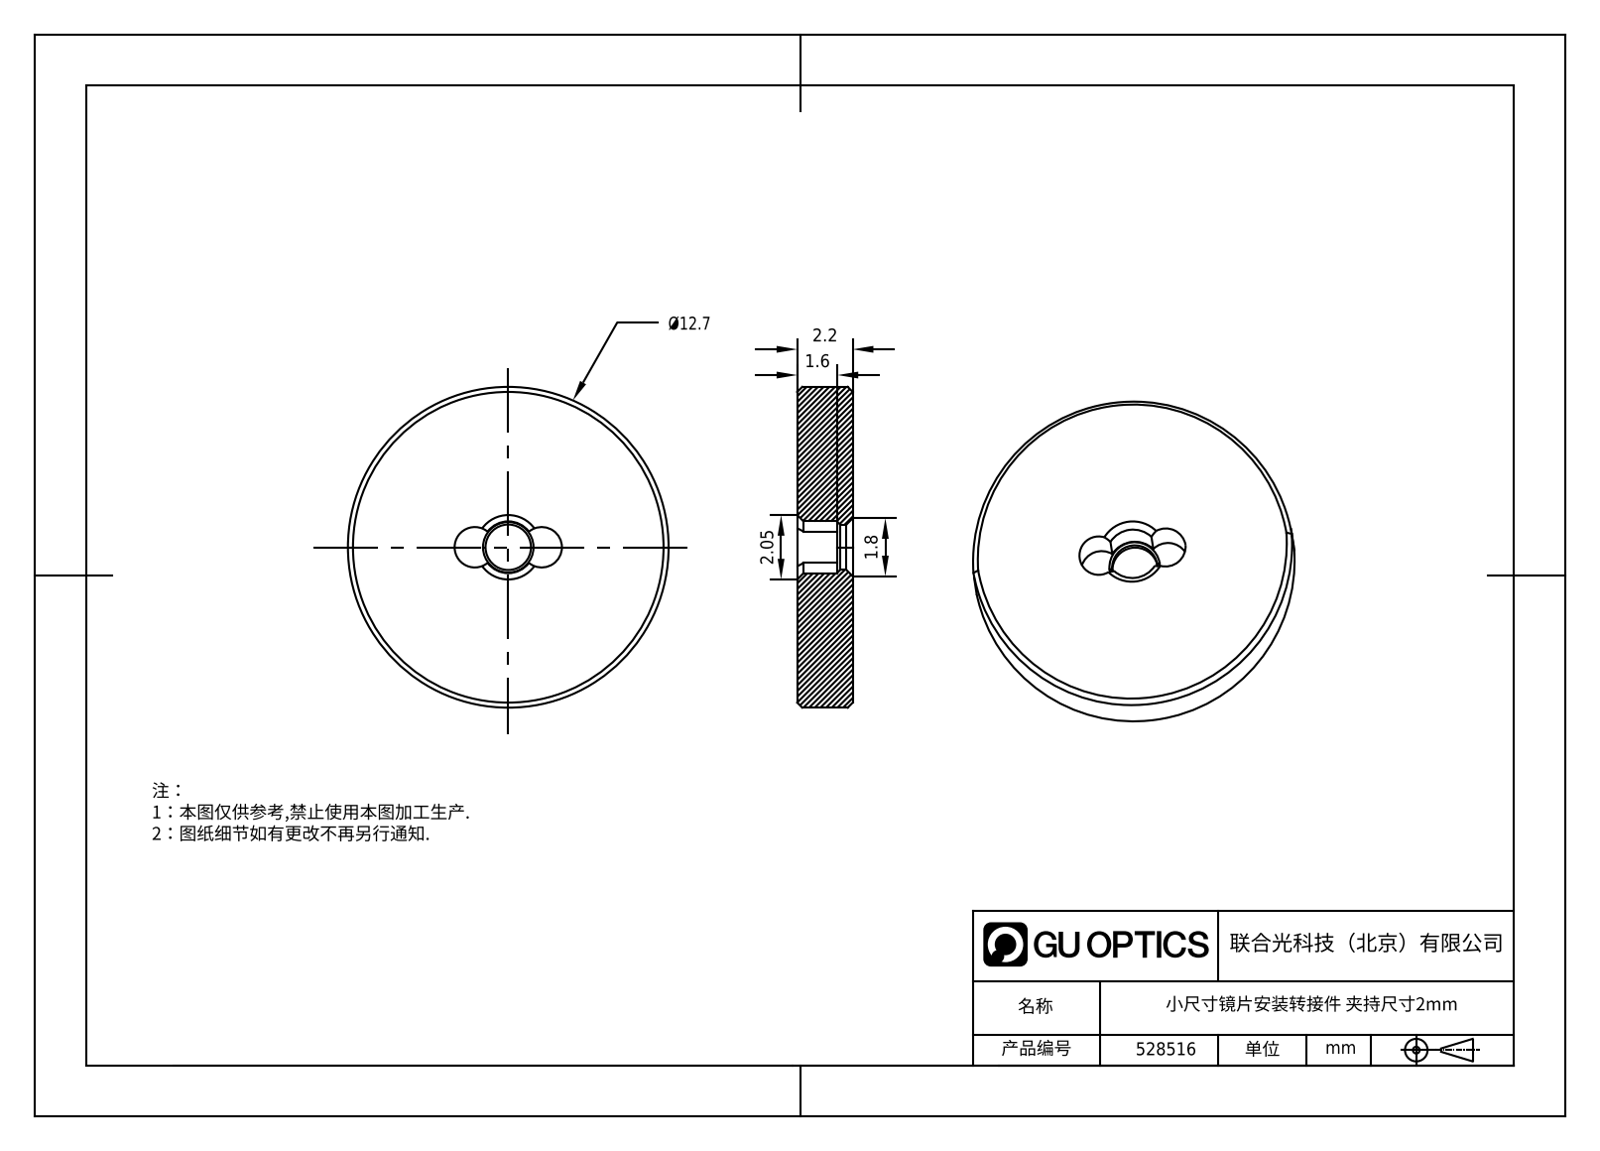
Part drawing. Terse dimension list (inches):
name: 1.6.4.2-ZSJ-05-2
written by: SolidWorks 2021 (CONFIG_CONTROL_DESIGN)
unit: in
bodies: 1 solid, 22 faces (3 planar, 9 cylindrical, 10 other)
size: 0.5 × 0.5 × 0.087
volume: 0.016 in³; area: 0.536 in²
holes: 1× ⌀0.071
bosses: 1× ⌀0.5
rounds: 2× R0.031, 1× R0.04
face distances: 0.087, 0.024, 0.063
